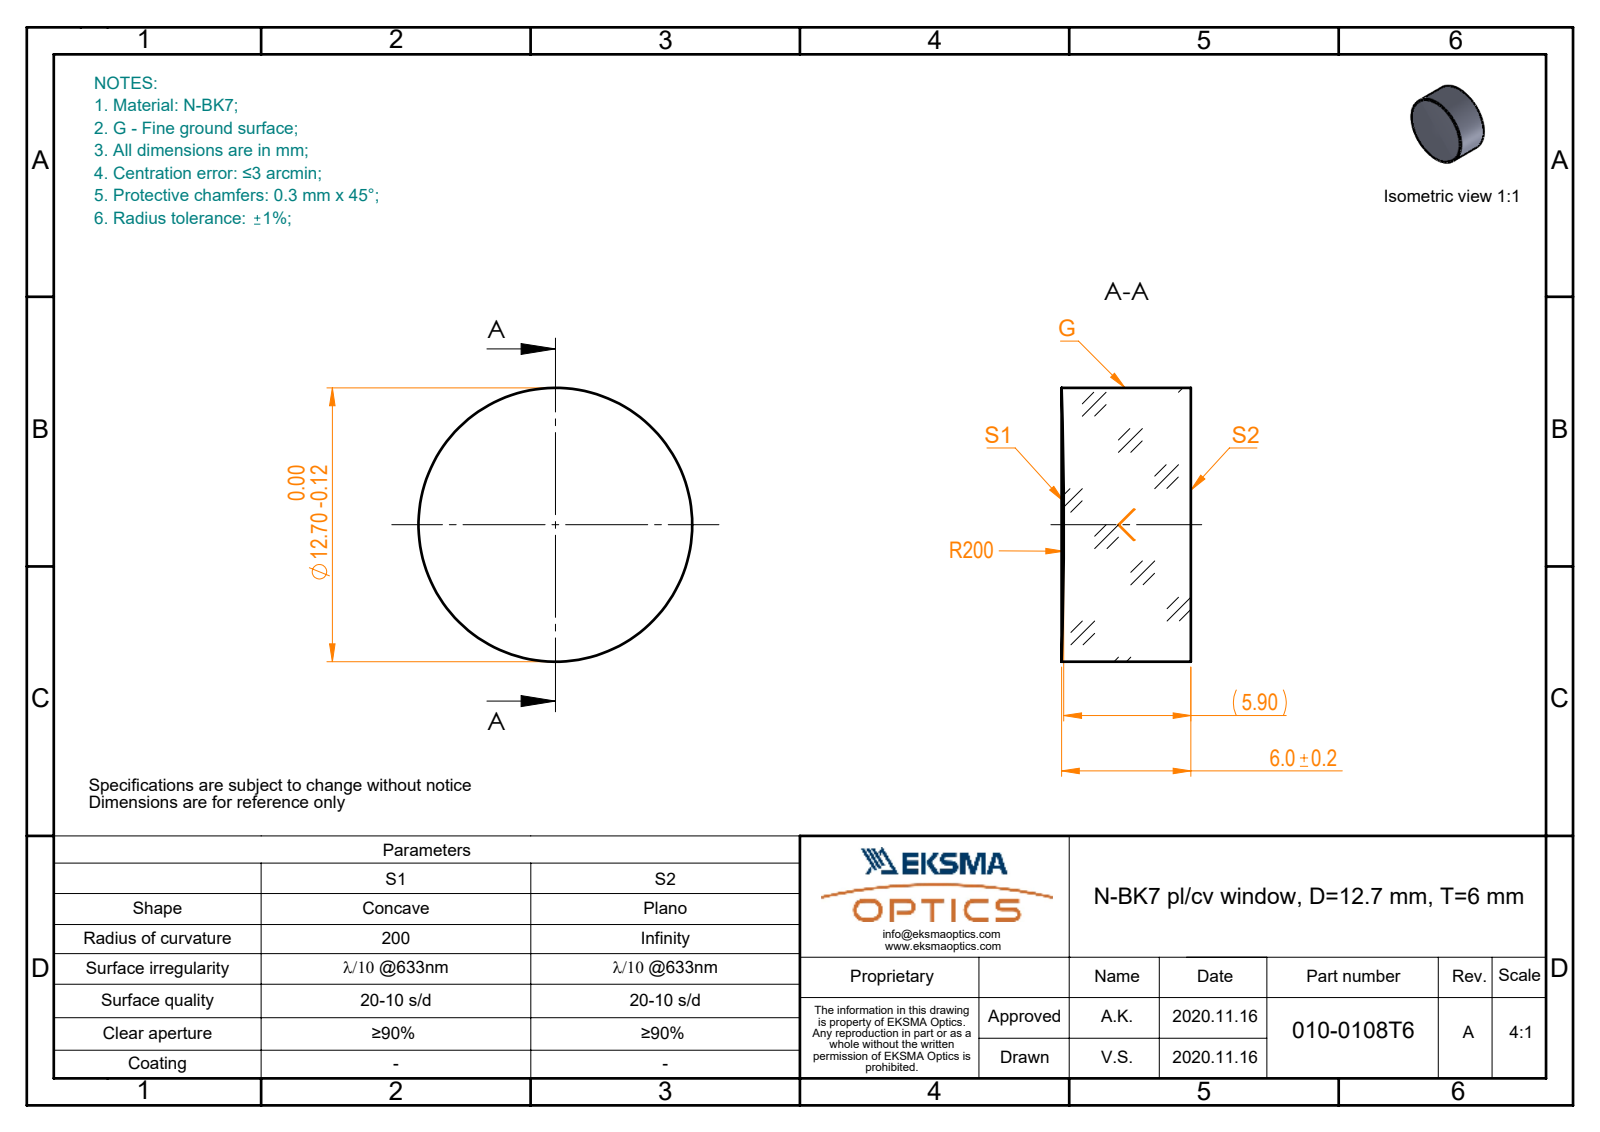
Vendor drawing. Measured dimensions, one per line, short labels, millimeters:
name: 010-0108T6_N-BK7_PCV_window
written by: SolidWorks 2019 (CONFIG_CONTROL_DESIGN)
unit: mm
bodies: 1 solid, 5 faces (1 planar, 2 cylindrical, 2 other)
size: 12.7 × 12.7 × 6
volume: 754 mm³; area: 493 mm²
bosses: 1× ⌀12.7
